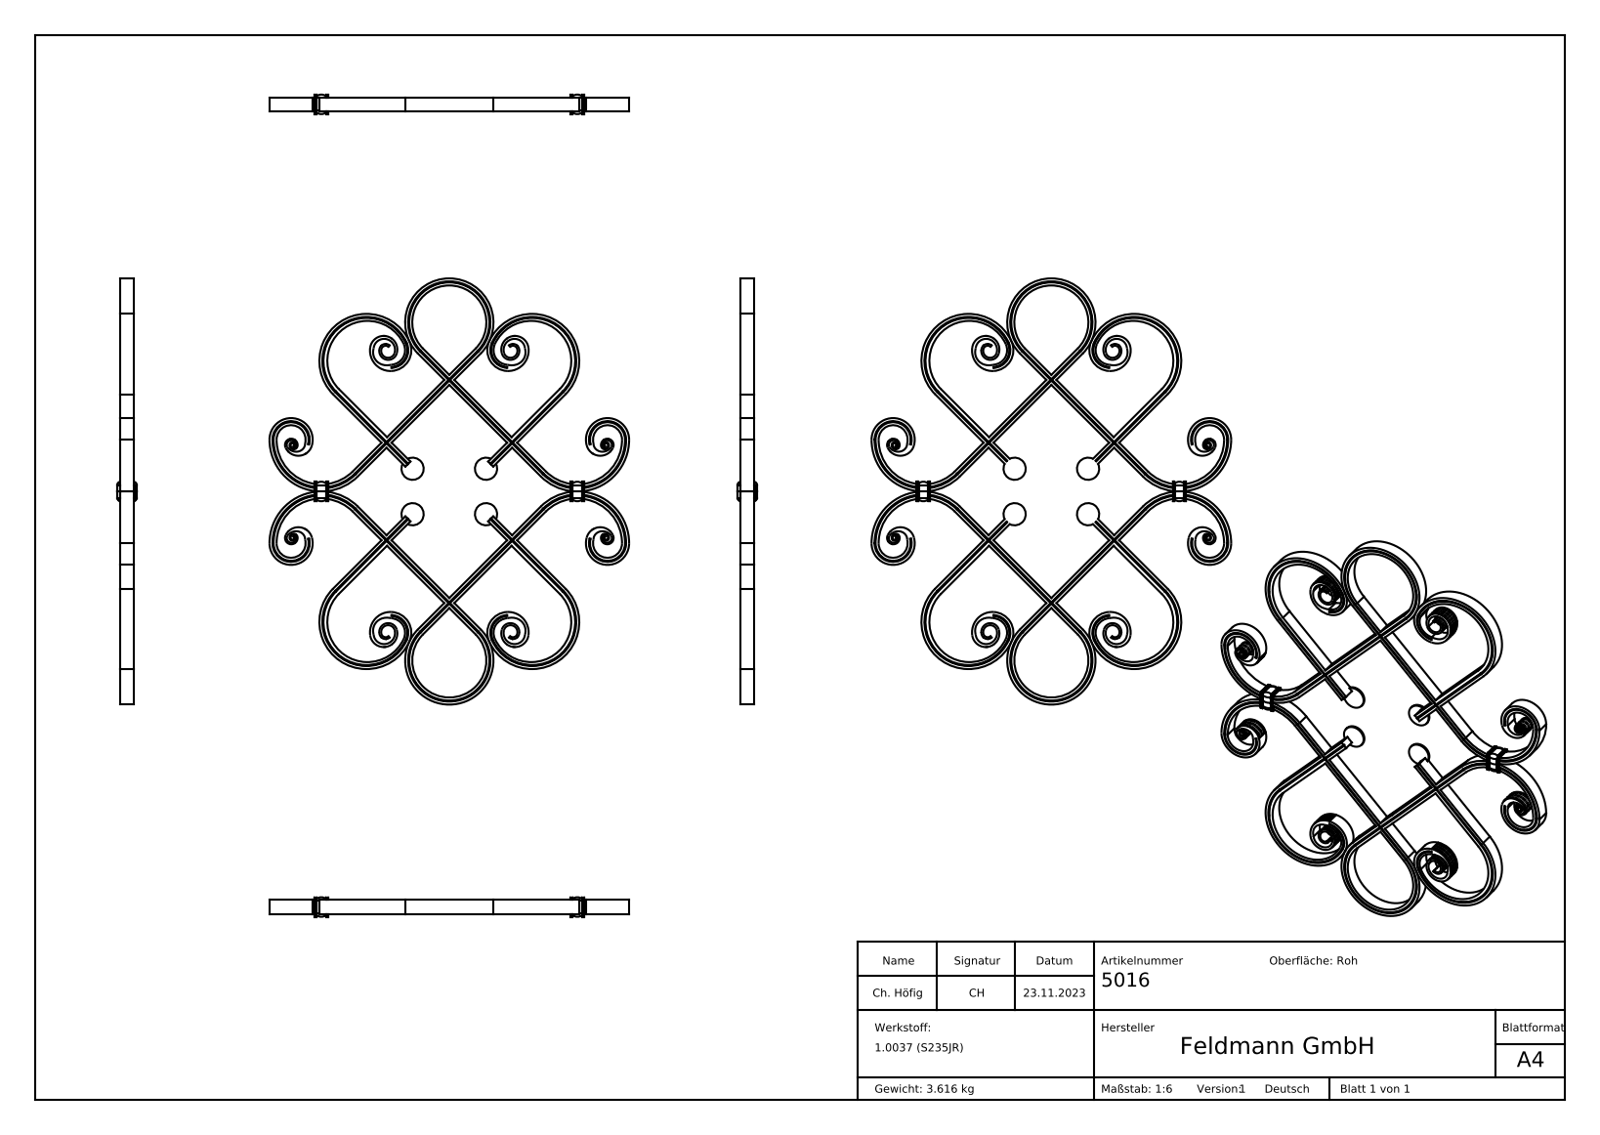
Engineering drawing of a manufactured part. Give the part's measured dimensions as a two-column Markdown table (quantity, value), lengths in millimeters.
| quantity | value |
| --- | --- |
| part name | 5016 |
| STEP written by | SolidWorks 2018 (CONFIG_CONTROL_DESIGN) |
| units | millimeters |
| bodies | 2 solids, 1096 faces (494 planar, 164 cylindrical, 438 other) |
| overall size | 480 × 405 × 22 |
| volume | 463 556 mm³ |
| surface area | 201 082 mm² |
| round bosses / shafts (diameter × count) | 25 × 4 |
| partial cylindrical surfaces (radius × count) | 0.25 × 56, 8.67 × 8, 4 × 4, 16.32 × 4, 16.4 × 4, 23.48 × 4, 24.32 × 4, 45.11 × 4 |
| main face-to-face distances | 16, 8, 177.68, 77.7, 107.98, 69.7, 99.98, 169.68, 185.68, 86.46 |
